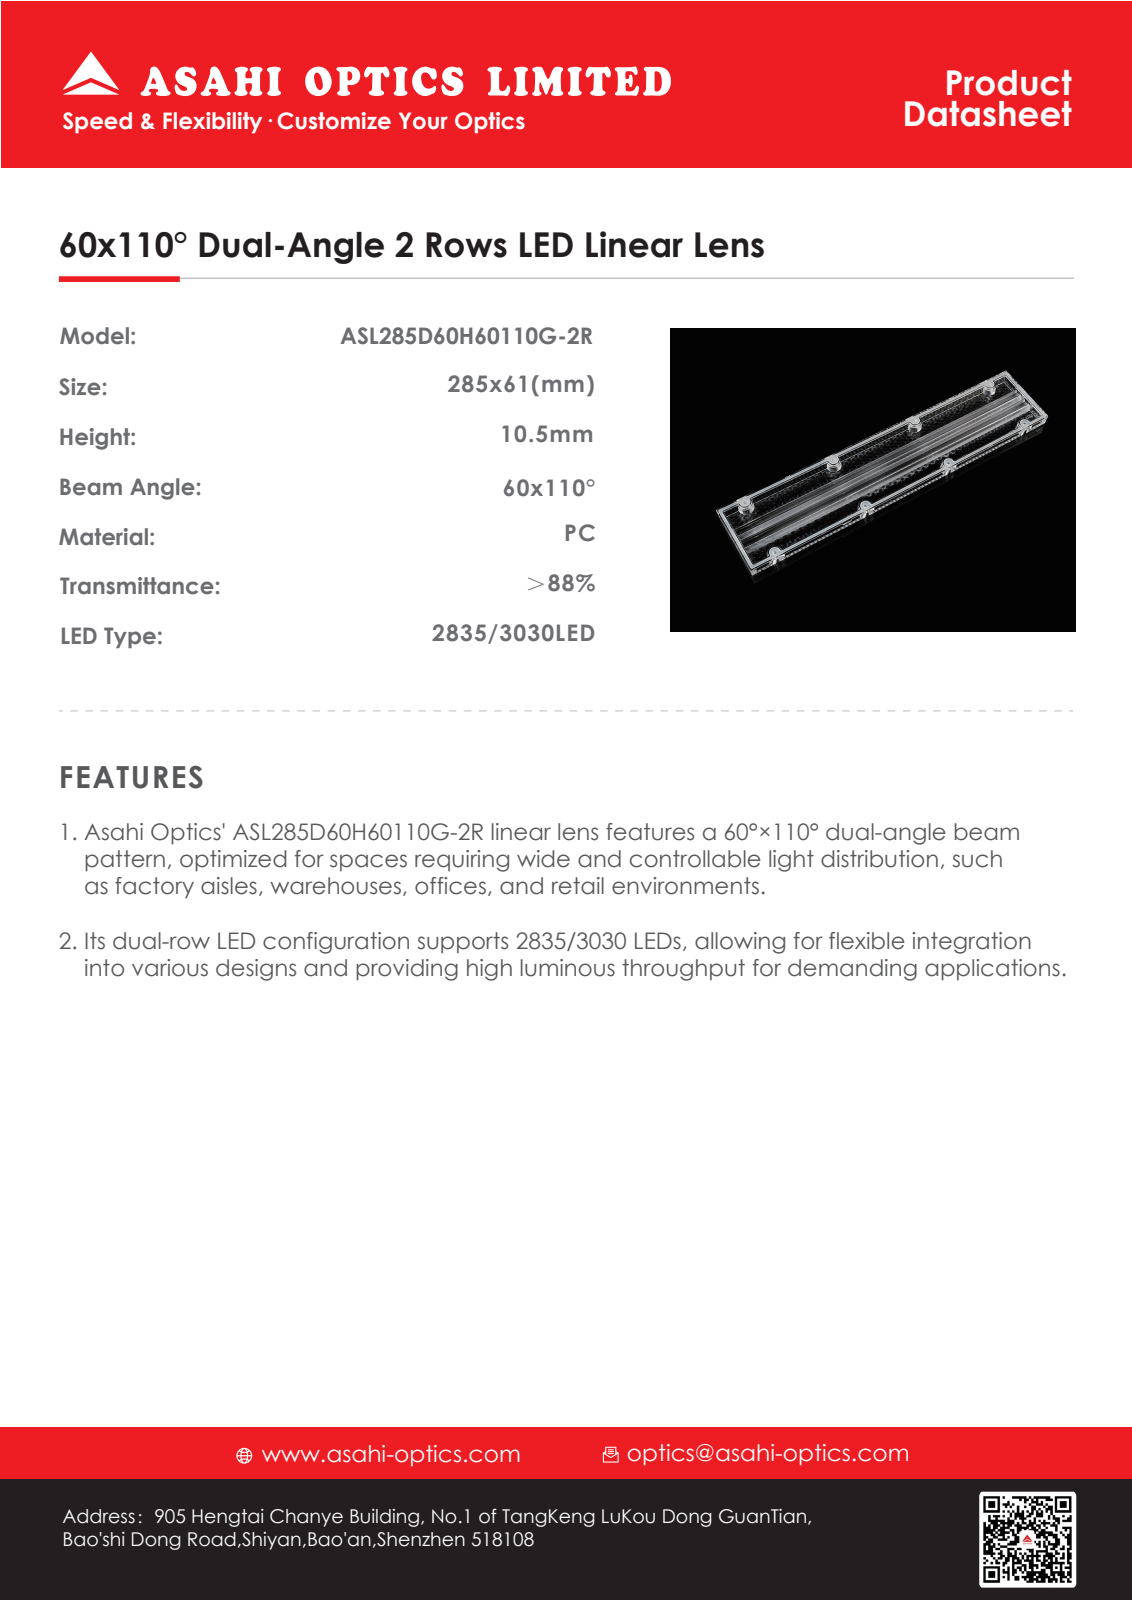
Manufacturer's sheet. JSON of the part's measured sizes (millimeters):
{"part_name": "Admi20C848F6alsg", "step_written_by": "SIEMENS PLM Software NX 10.0 (AP203_CONFIGURATION_CONTROLLED_3D_DESIGN_OF_MECHANICAL_PARTS_AND_ASSEMBLIES_MIM_LF)", "units": "millimeters", "bodies": {"solids": 3, "faces": 4641, "planar": 4179, "cylindrical": 219, "other": 243}, "overall_size": [285, 61, 11], "volume_mm3": 103996, "surface_area_mm2": 86239, "round_holes": [[3.2, 8]], "partial_cylinders_radius": [[1, 66], [1.5, 54], [0.3, 40], [19.72, 2], [4, 1]], "face_to_face_distances": [1.6, 10.5, 8.9, 4.5, 2.9, 6, 2.5, 56.36, 2.3, 0.7], "hole_center_spacings": [80, 94.87, 51, 160, 167.93, 240, 245.36]}
